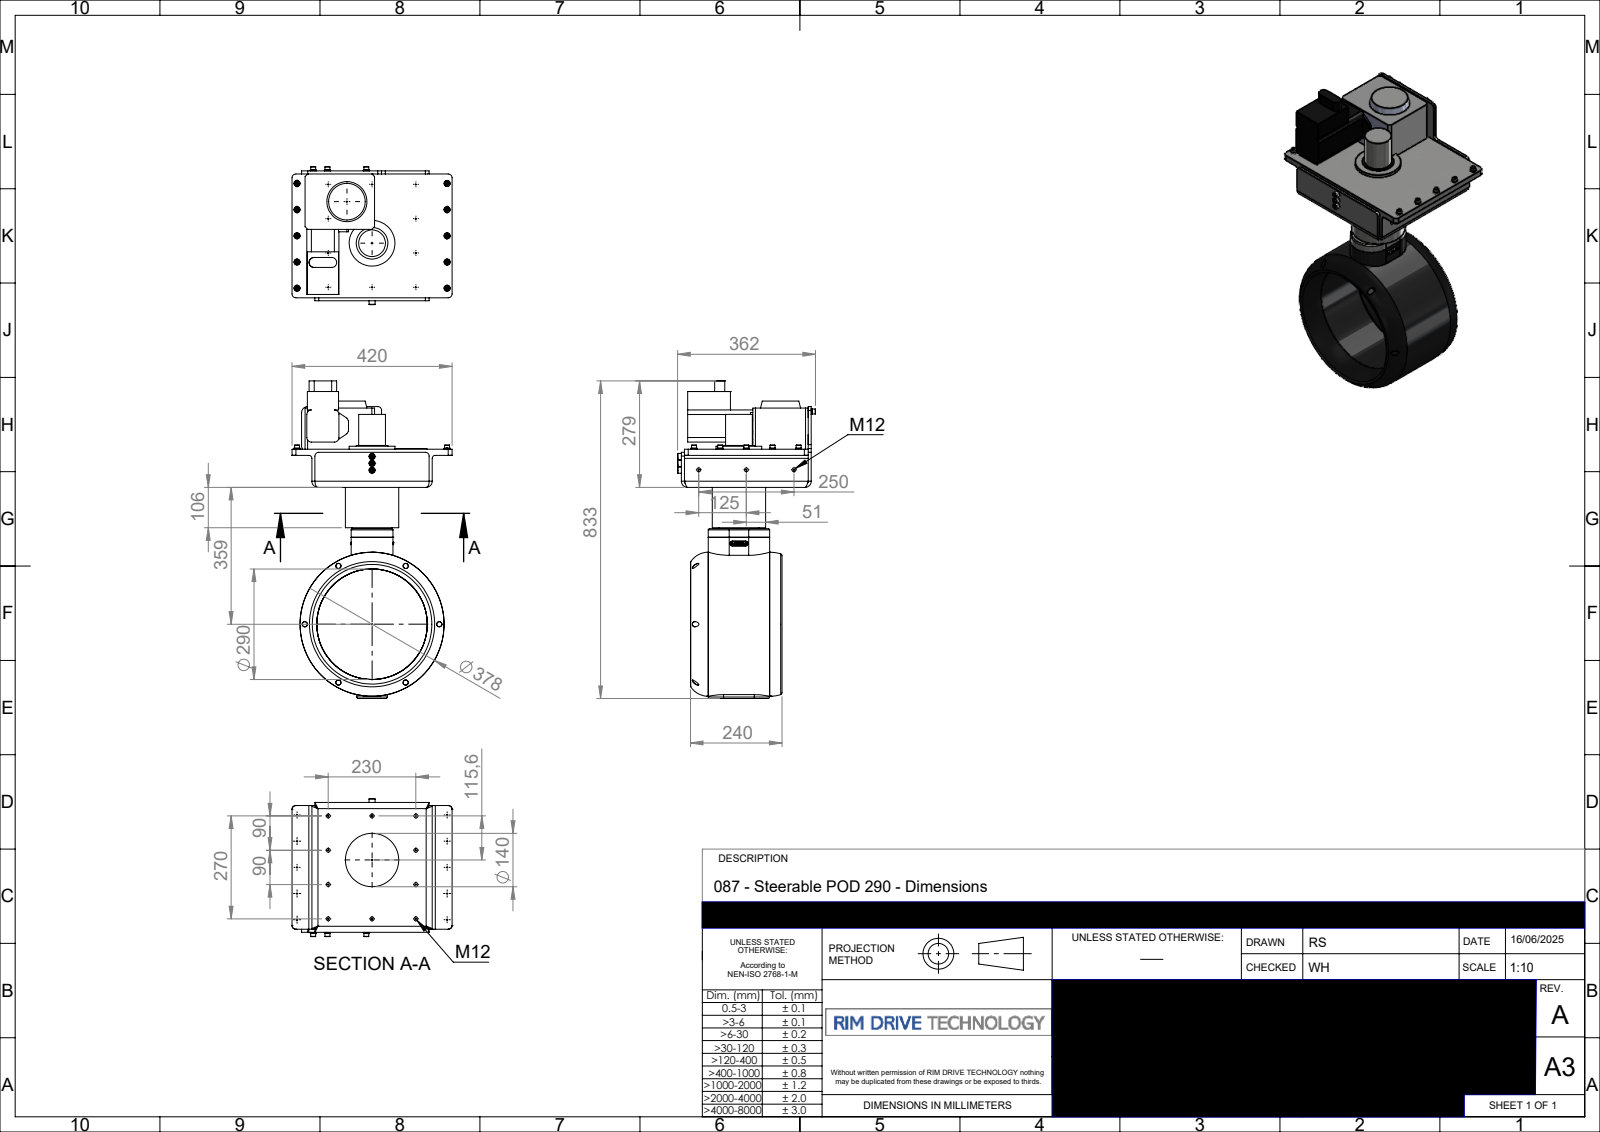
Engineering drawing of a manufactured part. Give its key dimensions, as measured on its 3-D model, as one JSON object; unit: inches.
{"part_name": "P-087-130-rev-A-M290", "step_written_by": "SolidWorks 2024 (AUTOMOTIVE_DESIGN)", "units": "inches", "bodies": {"solids": 1, "faces": 1140, "planar": 776, "cylindrical": 132, "other": 232}, "overall_size": [32.811, 16.535, 14.25], "volume_in3": 1779, "surface_area_in2": 1882, "round_holes": [[0.402, 13], [0.138, 2], [0.26, 2], [11.417, 1]], "round_bosses_or_shafts": [[0.63, 16], [0.583, 13], [0.512, 13], [0.456, 2], [0.236, 2], [0.224, 2], [14.882, 1], [5.512, 1]], "partial_cylinders_radius": [[0.394, 13], [0.63, 7], [0.157, 4], [0.197, 4], [0.472, 4], [0.315, 3], [0.004, 2], [0.118, 2]], "face_to_face_distances": [3.937, 0.63, 3.307, 4.252, 13.416, 0.315, 3.512, 12.441, 8.189, 4.882], "hole_center_spacings": [3.543, 9.724, 4.528, 5.749, 7.087, 8.409, 9.055, 11.498]}
